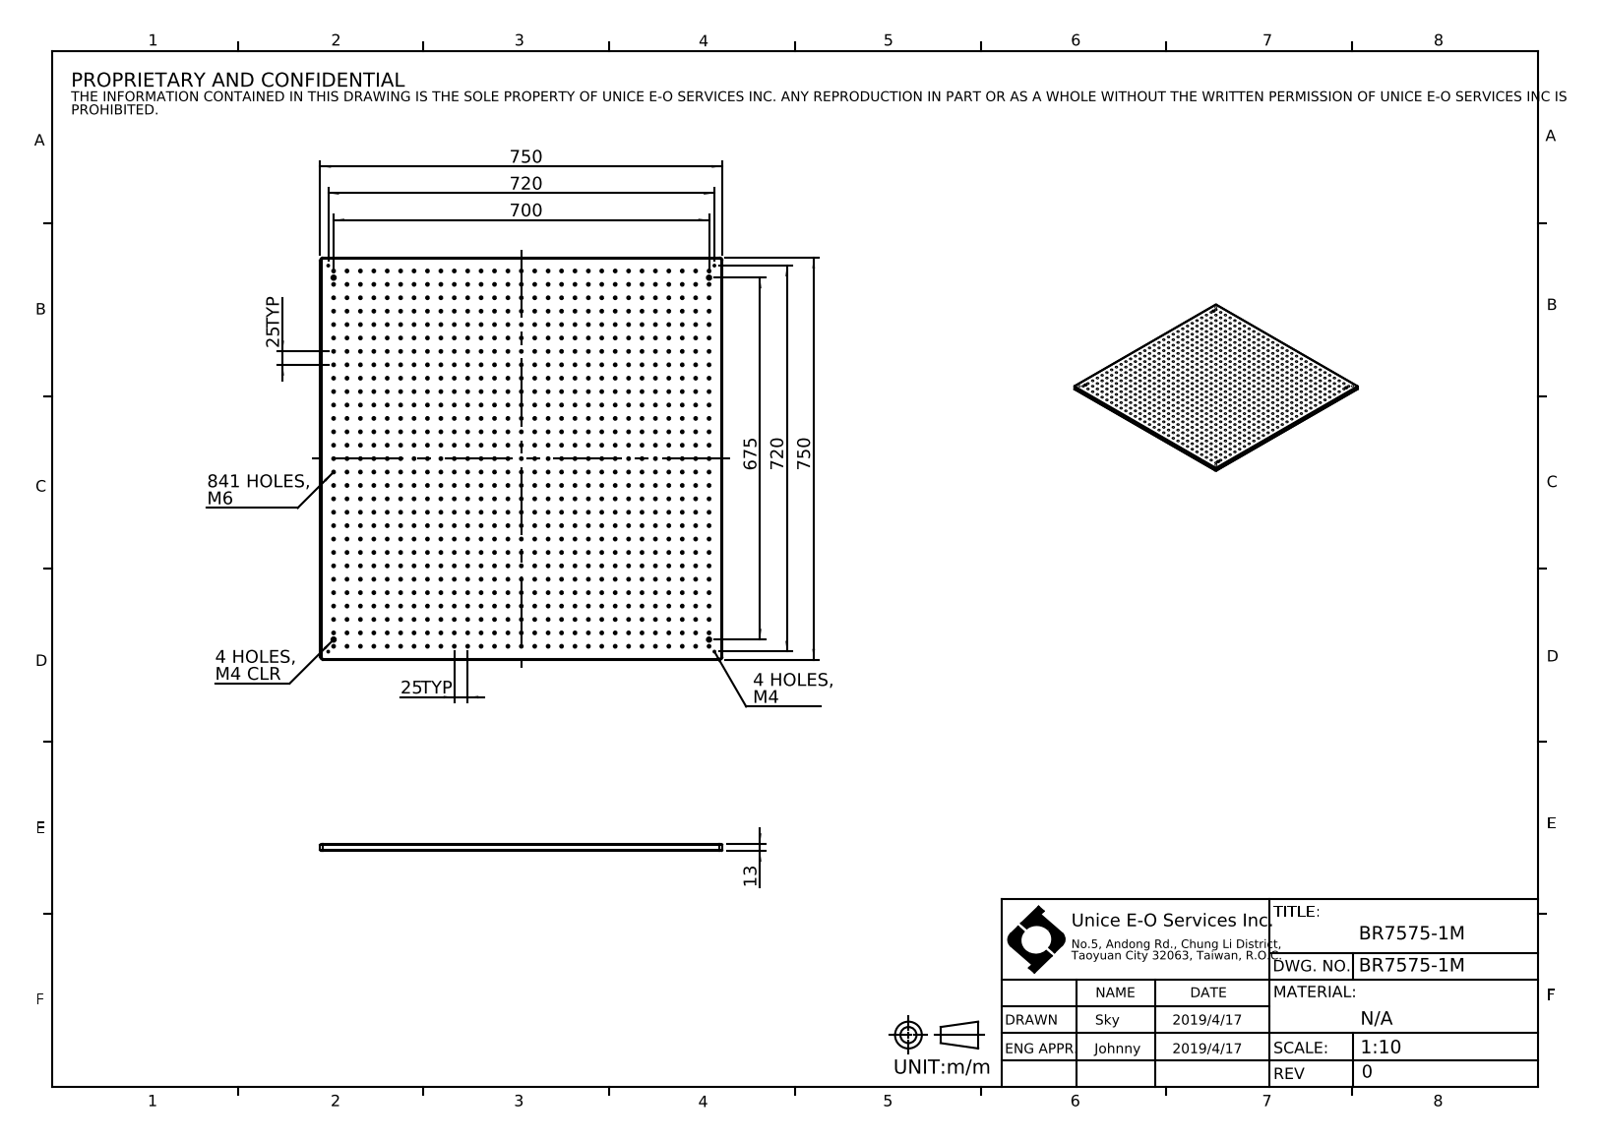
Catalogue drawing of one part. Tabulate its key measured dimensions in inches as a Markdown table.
| quantity | value |
| --- | --- |
| part name | U-F1-BR7575-1M-D0; BR7575-1M |
| STEP written by | SolidWorks 2016 (AUTOMOTIVE_DESIGN) |
| units | inches |
| bodies | 1 solid, 1736 faces (10 planar, 1718 cylindrical, 8 other) |
| overall size | 29.528 × 29.528 × 0.512 |
| volume | 432.7 in³ |
| surface area | 2 013 in² |
| round holes (diameter × count) | 0.197 × 841, 0.13 × 4, 0.177 × 4, 0.315 × 4 |
| partial cylindrical surfaces (radius × count) | 0.079 × 8, 0.197 × 4 |
| main face-to-face distances | 0.512, 29.528, 0.339, 0.173 |
| hole center spacings | 0.984, 1.969, 2.953, 1.392, 2.201, 3.937, 3.113, 4.058 |
